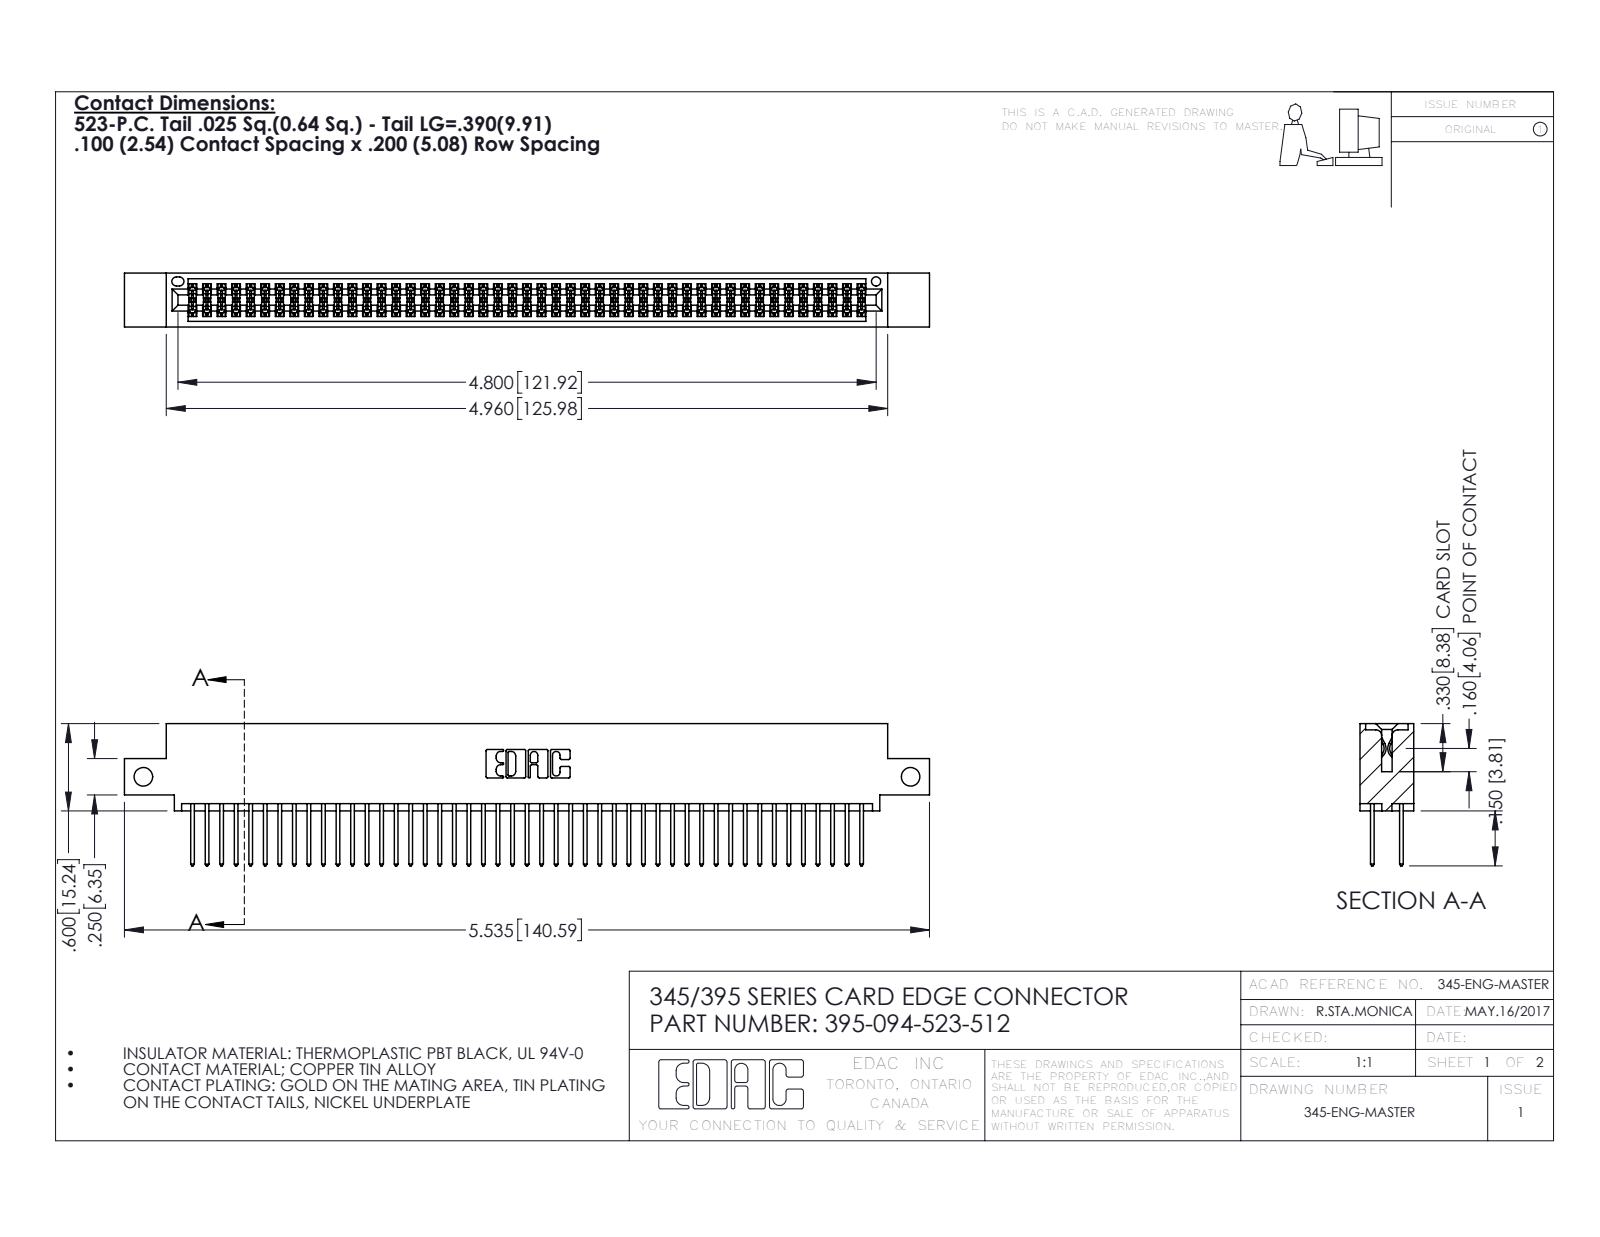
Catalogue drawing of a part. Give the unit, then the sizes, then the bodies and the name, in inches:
Units: inches
Overall size (bounding box): 5.535 × 0.977 × 0.37
Round holes (diameter × count): ⌀0.128 ×2, ⌀0.064 ×1
Partial cylindrical surfaces — rounded edges, fillets, slot ends (radius × count): R0.006 ×141, R0.01 ×94, R0.01 ×22, R0.007 ×6, R0.031 ×6, R0.026 ×3, R0.014 ×2, R0.019 ×2
Main face-to-face distances: 0.298, 0.072, 0.2, 0.098, 0.272, 0.025, 0.37, 0.225, 0.175, 0.149
Hole centre spacings: 5.275
Volume: 0.838 in³ · Surface area: 32.89 in²
Bodies: 95 solids, 4830 faces (3186 planar, 1644 cylindrical, 0 other)
Part name (STEP PRODUCT): 395-094-523-512; 345 Part_0.110 Offset - Side Mount; 345-292-001_345-293-123
STEP written by: SolidWorks 2016 (CONFIG_CONTROL_DESIGN)
